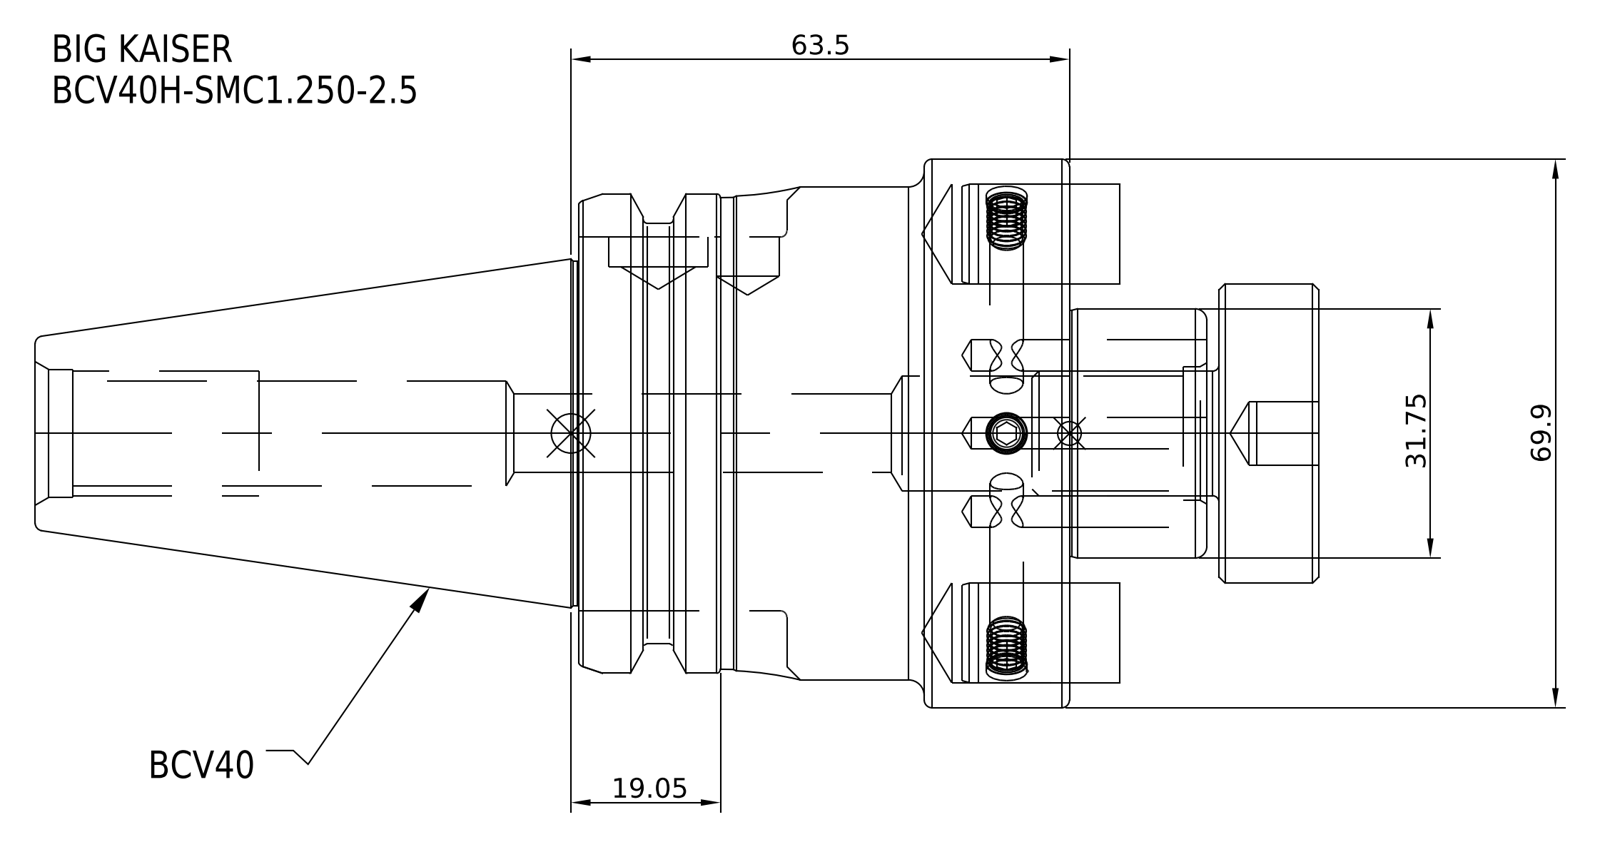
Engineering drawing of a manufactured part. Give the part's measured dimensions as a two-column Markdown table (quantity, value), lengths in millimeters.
| quantity | value |
| --- | --- |
| part name | BCV40H-SMC1_250-2_5 |
| STEP written by | SolidWorks 2021 (CONFIG_CONTROL_DESIGN) |
| units | millimeters |
| bodies | 1 solid, 43 faces (17 planar, 16 cylindrical, 10 other) |
| overall size | 138.15 × 69.9 × 69.9 |
| volume | 271 092 mm³ |
| surface area | 29 404 mm² |
| round holes (diameter × count) | 14.68 × 1 |
| round bosses / shafts (diameter × count) | 69.9 × 1, 63.5 × 1, 62.8 × 1, 62.4 × 1, 56.36 × 1, 44.45 × 1 |
| main face-to-face distances | 62.5, 18.5, 44, 131.75, 113.25, 69.25, 12.7, 6.4, 24.9, 68.9 |
